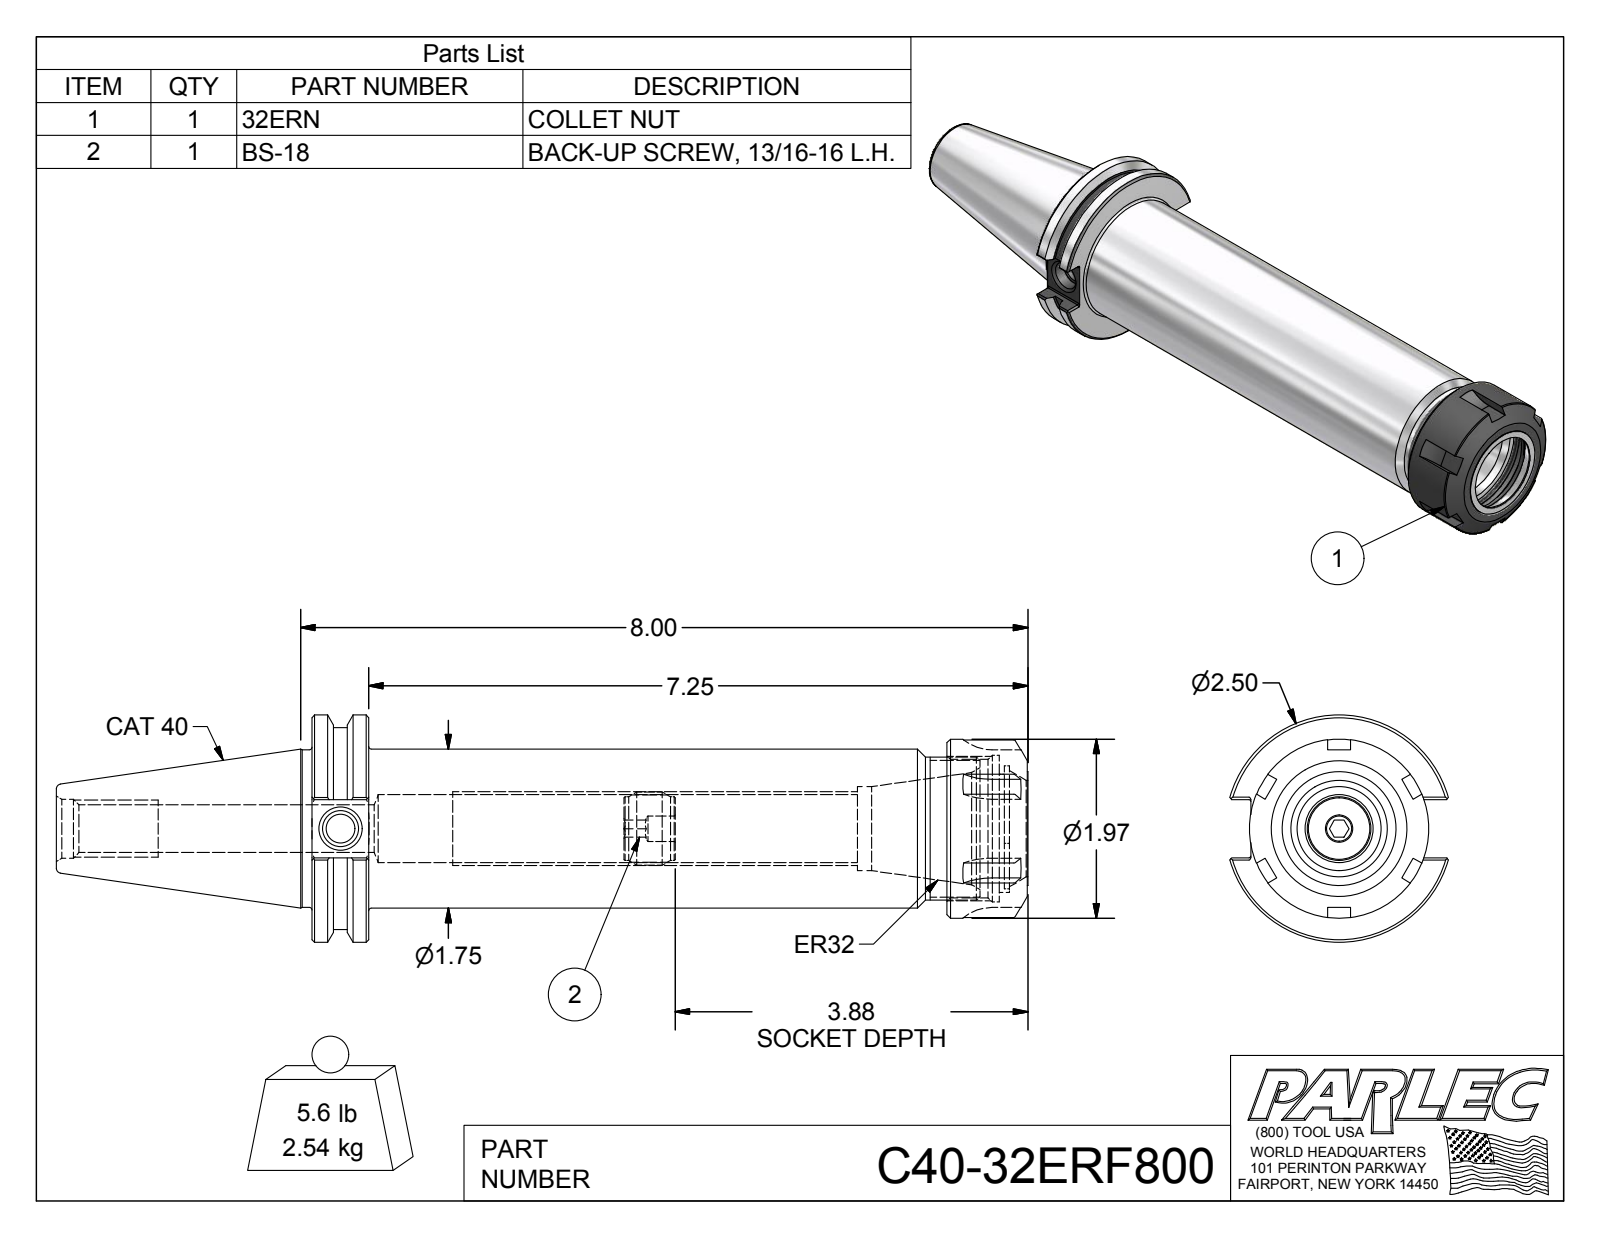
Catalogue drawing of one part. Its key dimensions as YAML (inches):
part_name: "C40-32ERF800; C40-32ER8-1; 32ERN; BS-18"
step_written_by: "Autodesk Inventor 2012 (AUTOMOTIVE_DESIGN)"
units: inches
bodies: {solids: 3, faces: 148, planar: 64, cylindrical: 44, other: 40}
overall_size: [10.688, 2.5, 2.403]
volume: 19.74
surface_area: 100.2
round_holes:
  - {diameter: 0.28, count: 1}
  - {diameter: 0.315, count: 1}
  - {diameter: 0.399, count: 1}
  - {diameter: 0.527, count: 1}
  - {diameter: 0.648, count: 1}
  - {diameter: 0.745, count: 1}
  - {diameter: 0.925, count: 1}
  - {diameter: 1.063, count: 1}
  - {diameter: 1.299, count: 1}
  - {diameter: 1.522, count: 1}
  - {diameter: 1.614, count: 1}
round_bosses_or_shafts:
  - {diameter: 2.5, count: 1}
  - {diameter: 2.219, count: 1}
  - {diameter: 1.969, count: 1}
  - {diameter: 1.75, count: 1}
  - {diameter: 1.73, count: 1}
  - {diameter: 1.575, count: 1}
  - {diameter: 1.252, count: 1}
  - {diameter: 0.805, count: 1}
partial_cylinders:
  - {radius: 0.02, count: 12}
  - {radius: 0.5, count: 6}
  - {radius: 0.689, count: 1}
face_to_face_distances: [0.625, 6.984, 6.359, 7.563, 6.938, 0.579, 7.87, 7.245, 0.886, 0.307]
hole_center_spacings: [0.059]
